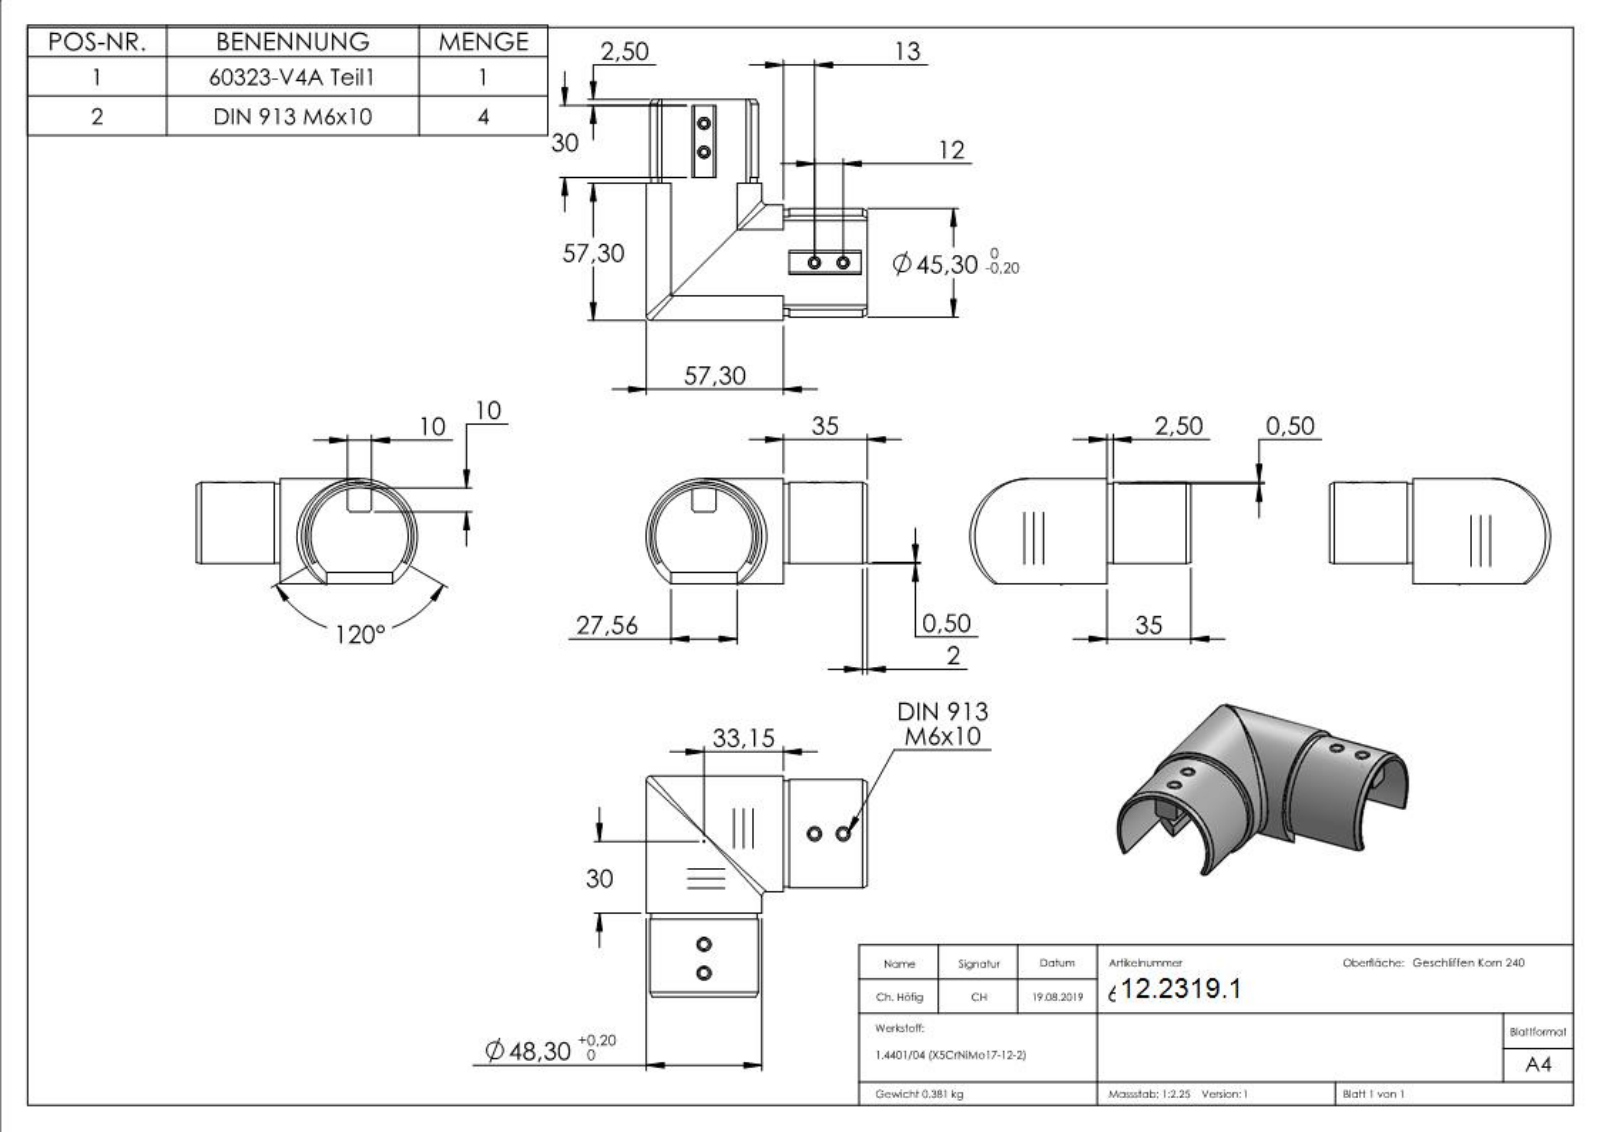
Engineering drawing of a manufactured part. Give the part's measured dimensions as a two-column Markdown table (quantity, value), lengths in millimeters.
| quantity | value |
| --- | --- |
| part name | DIN913_DIN 913 M6x10; 6032X-240 Teil1 Konfig Verlaufecke Nutrohr_60323-V4A Teil1; 60323-V4A |
| STEP written by | SolidWorks 2015 (CONFIG_CONTROL_DESIGN) |
| units | millimeters |
| bodies | 5 solids, 392 faces (212 planar, 40 cylindrical, 140 other) |
| overall size | 92.3 × 92.3 × 44.18 |
| volume | 47 607 mm³ |
| surface area | 32 048 mm² |
| round holes (diameter × count) | 5 × 4 |
| round bosses / shafts (diameter × count) | 6 × 4, 48.3 × 2 |
| partial cylindrical surfaces (radius × count) | 20.35 × 2, 22.15 × 2, 22.65 × 2 |
| main face-to-face distances | 8.78, 18.78, 10, 38.15, 28.15, 2.5, 46.93, 32.5, 49.43, 40.65 |
| hole center spacings | 12, 74.24, 65.27, 82.24 |
